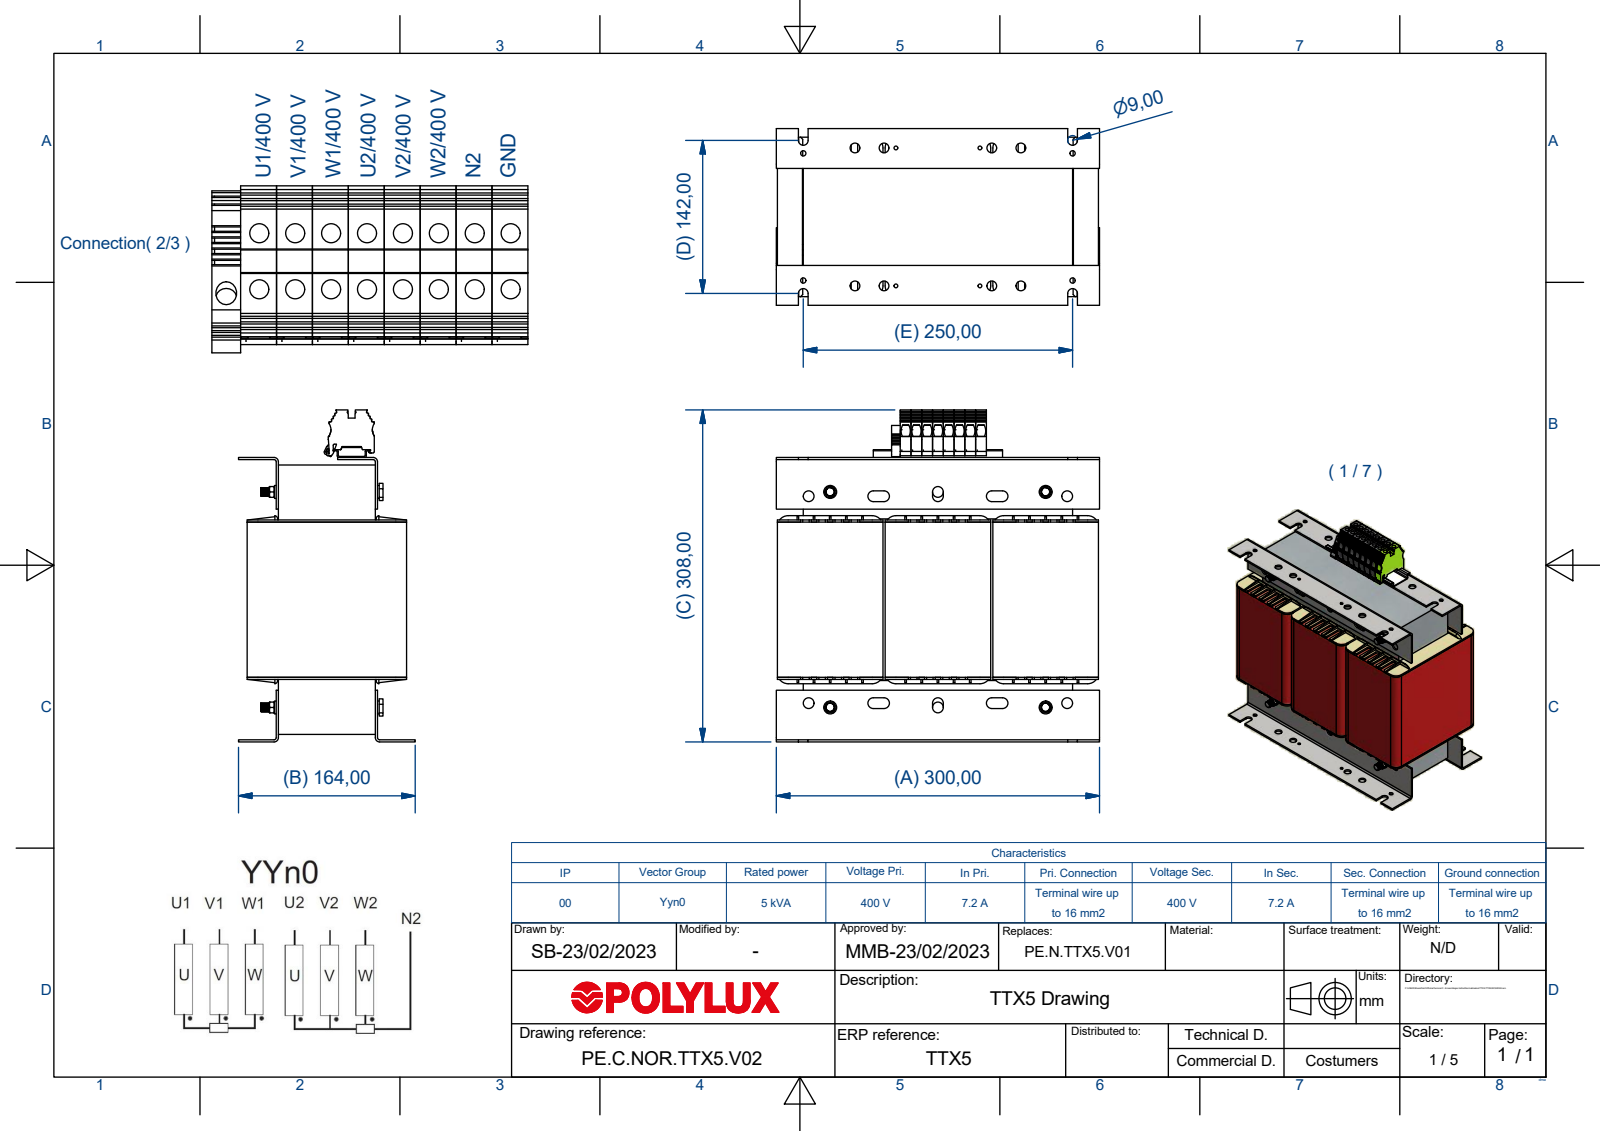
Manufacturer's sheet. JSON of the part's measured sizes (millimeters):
{"part_name": "TTX5; Núcleo RC50x90; BRI50-3IP0E25; DIN 934 - M6 x 1 (+8 more)", "step_written_by": "Autodesk Inventor 2018 (AUTOMOTIVE_DESIGN)", "units": "millimeters", "bodies": {"solids": 38, "faces": 2672, "planar": 1898, "cylindrical": 726, "other": 48}, "overall_size": [308.11, 300, 164], "volume_mm3": 8856000, "surface_area_mm2": 1313000, "round_holes": [[5.3, 16], [9, 12], [4.92, 10], [10, 10], [3.5, 6], [6.4, 4], [3, 2], [5.8, 2]], "round_bosses_or_shafts": [[12, 4], [6, 4]], "partial_cylinders_radius": [[0.5, 33], [3, 28], [11, 18], [10, 16], [1, 12], [0.3, 10], [5, 10], [0.1, 9]], "face_to_face_distances": [2, 100, 76, 24, 92, 98, 22, 176, 200, 1.25], "hole_center_spacings": [128, 92, 100, 11, 27, 36, 38, 48.26]}
